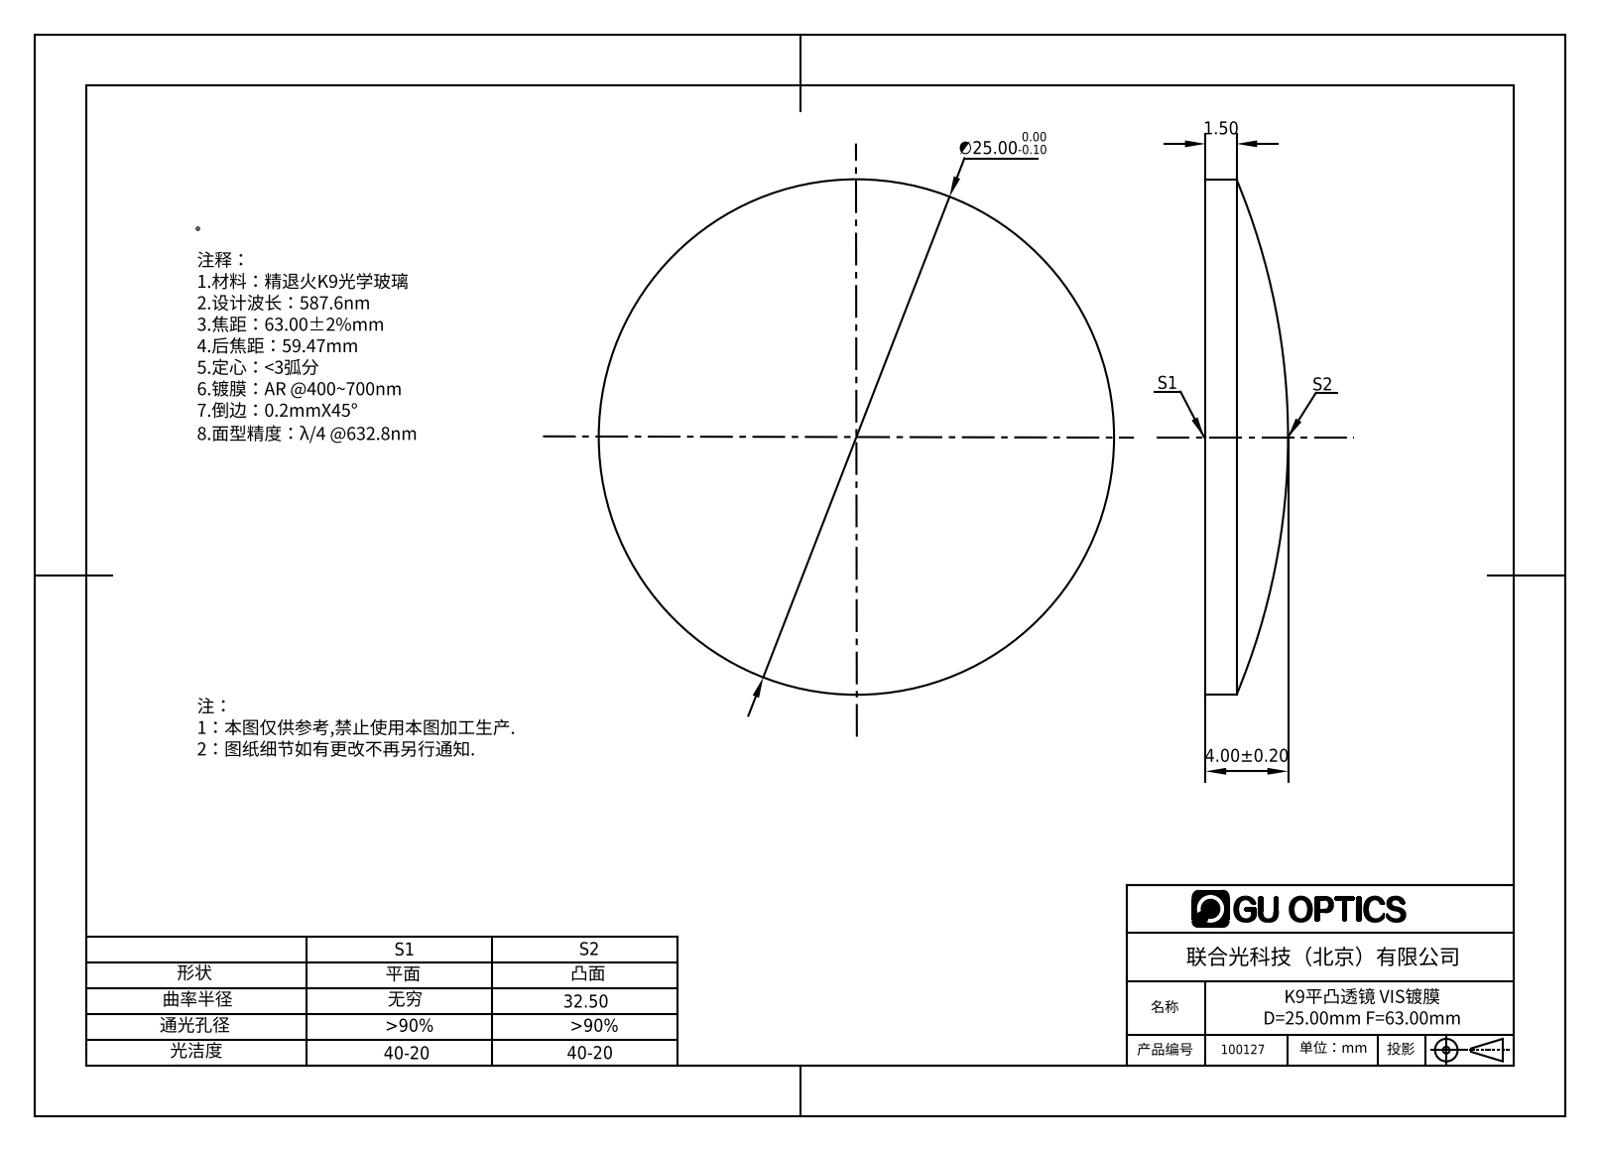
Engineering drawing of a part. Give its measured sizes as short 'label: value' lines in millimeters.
name: 100127
written by: SolidWorks 2016 (AUTOMOTIVE_DESIGN)
unit: mm
bodies: 1 solid, 5 faces (1 planar, 2 cylindrical, 2 other)
size: 25 × 25 × 4
volume: 1 358 mm³; area: 1 119 mm²
bosses: 1× ⌀25
